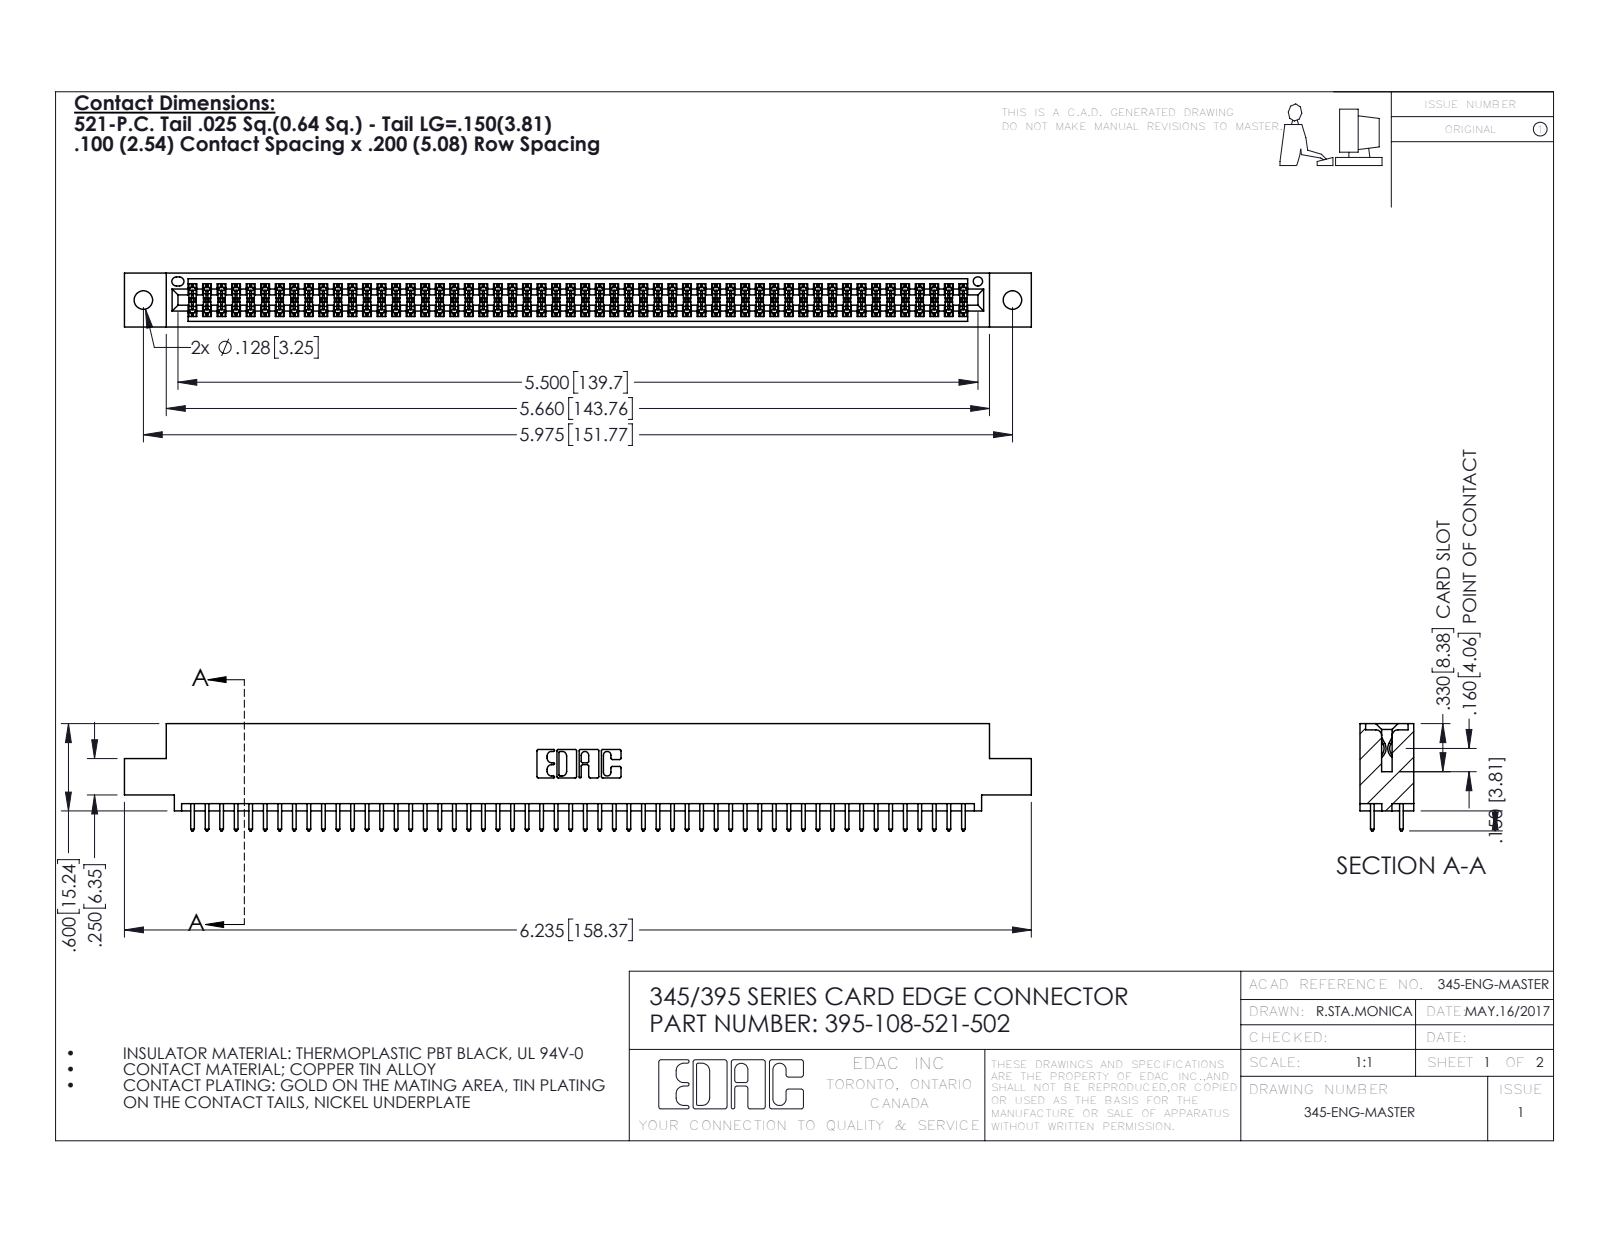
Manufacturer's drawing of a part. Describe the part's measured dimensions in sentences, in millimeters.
The part is named "345-292-001_345-293-121; 395-108-521-502; 345 Part_0.110 Offset - 0.128 Dia". Its 3-D file was written by "SolidWorks 2016 (CONFIG_CONTROL_DESIGN)". It is 109 solids with 5530 faces: 3648 planar, 1882 cylindrical and 0 other. Overall it measures 158.4 by 18.7 by 9.4 millimeters. Its volume is 15 300 cubic millimeters and its surface area 22 450 square millimeters. Round holes: 2 of diameter 3.3, 1 of diameter 1.6. Partial cylindrical surfaces (rounded edges, fillets, slot ends): 162 of radius 0.2, 108 of radius 0.3, 22 of radius 0.3, 6 of radius 0.2, 6 of radius 0.8, 3 of radius 0.7, 2 of radius 0.4, 2 of radius 0.5. The main face-to-face distances are 7.6, 1.8, 5.1, 2.5, 6.9, 0.6, 9.4, 5.7, 4.4, 3.8. The hole center spacings are 6.9, 145.8, 151.8.
